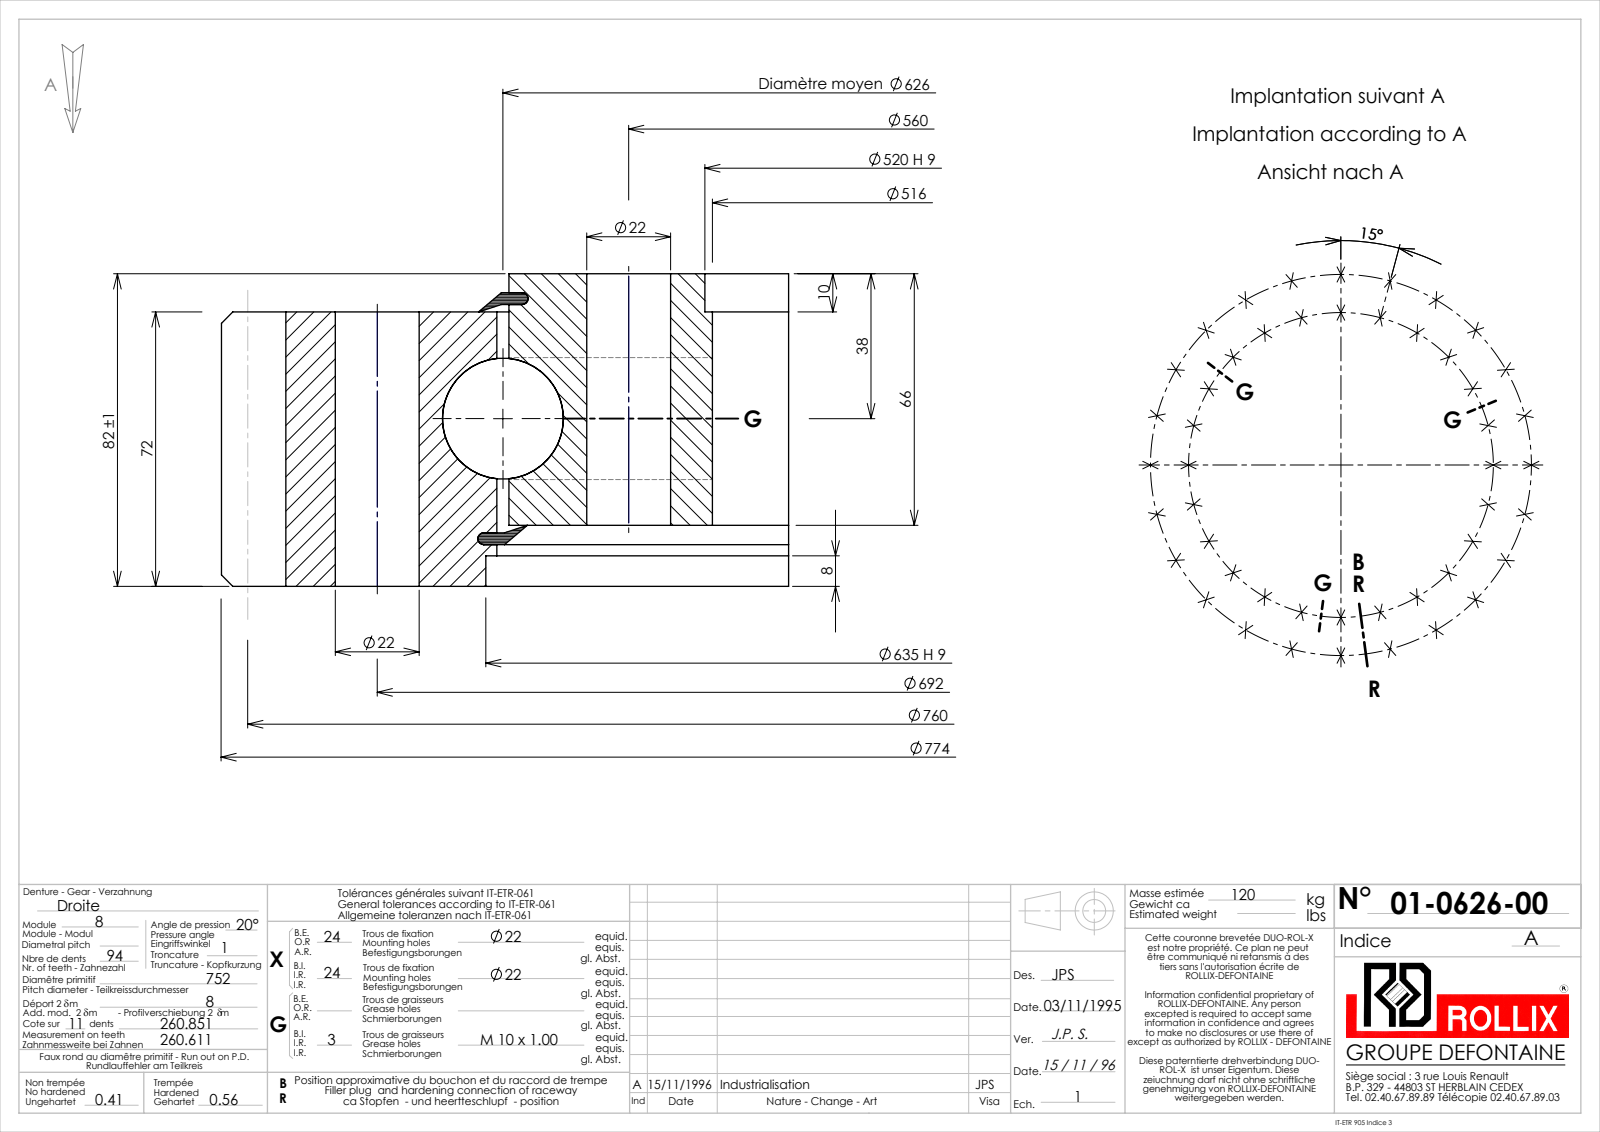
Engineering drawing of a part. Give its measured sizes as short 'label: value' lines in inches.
name: 01-0626-00
written by: SolidWorks 2016 (CONFIG_CONTROL_DESIGN)
unit: in
bodies: 5 solids, 727 faces (202 planar, 309 cylindrical, 216 other)
size: 30.472 × 30.465 × 3.228
volume: 844 in³; area: 2 469 in²
holes: 48× ⌀0.866, 3× ⌀0.354, 1× ⌀20.315, 1× ⌀20.472, 1× ⌀24.771, 1× ⌀25
bosses: 1× ⌀24.521, 1× ⌀24.52
rounds: 1× R14.567, 1× R15.236
face distances: 2.835, 0.63, 2.205, 3.228, 2.598, 0.394, 0.199, 2.404, 0.122, 0.077
hole spacings: 13.622, 7.051, 16.585, 21.614, 23.594, 26.316, 3.556, 10.426
